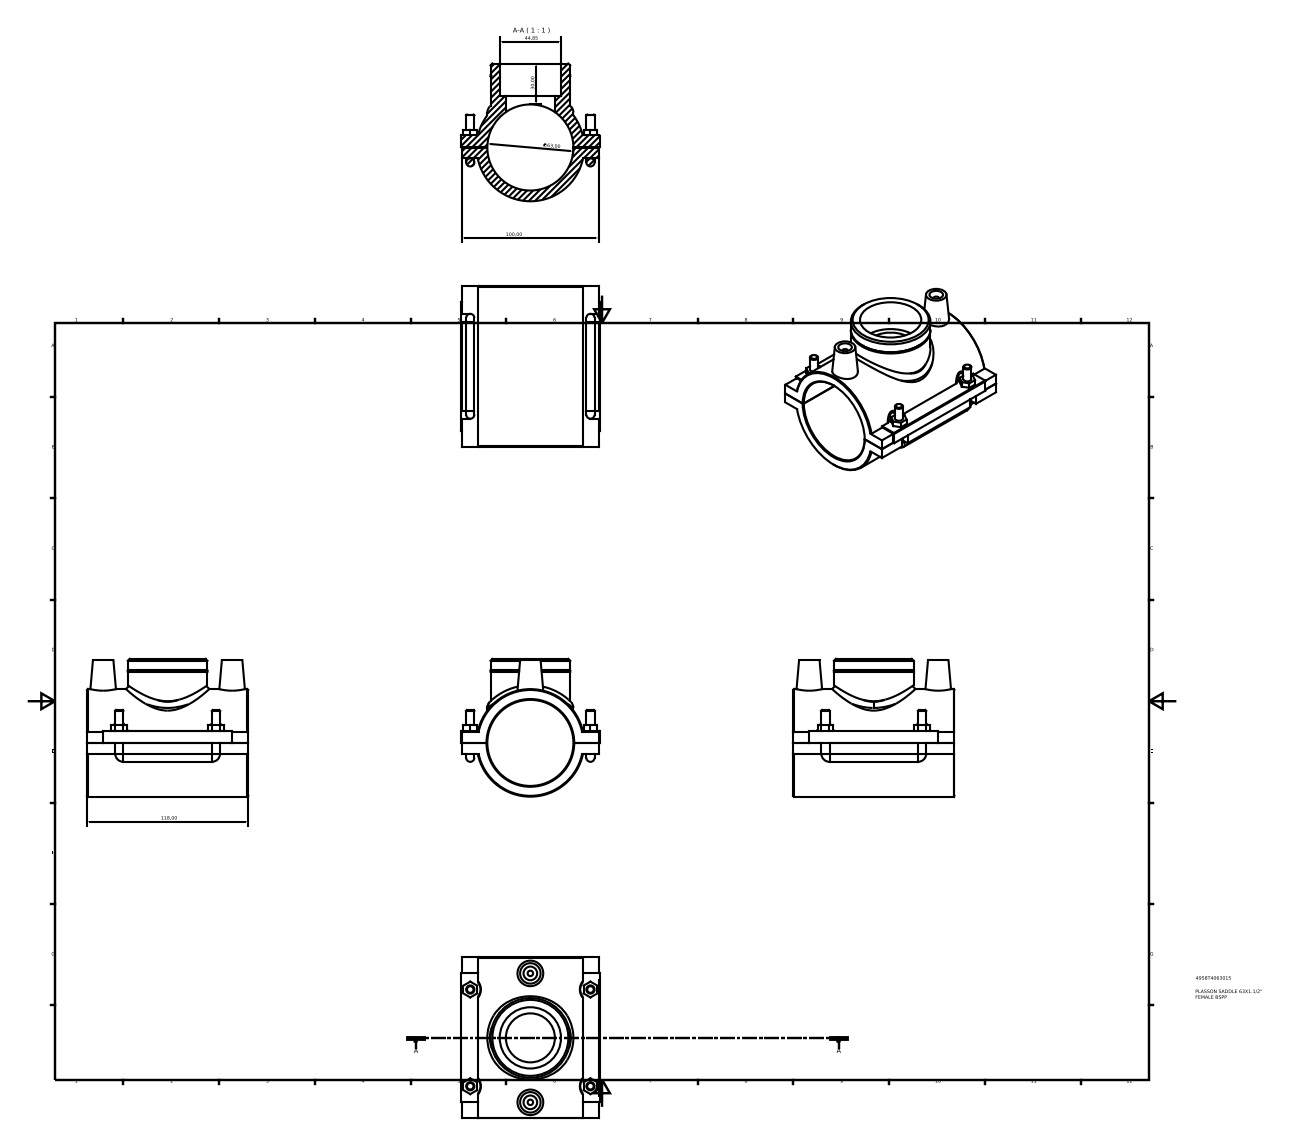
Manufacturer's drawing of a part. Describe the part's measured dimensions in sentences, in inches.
The part is named "4958T4063015". Its 3-D file was written by "Autodesk Inventor 2015 (AUTOMOTIVE_DESIGN)". It is 1 solid with 142 faces: 82 planar, 34 cylindrical and 26 other. Overall it measures 4.646 by 4.016 by 3.972 inches. Its volume is 17.49 cubic inches and its surface area 133.5 square inches. Round holes: 2 of diameter 0.394, 1 of diameter 1.413, 1 of diameter 1.765, 1 of diameter 2.48. Round bosses or shafts: 6 of diameter 0.236, 2 of diameter 0.157, 1 of diameter 3.1, 1 of diameter 2.295, 1 of diameter 2.256. Partial cylindrical surfaces (rounded edges, fillets, slot ends): 4 of radius 0.295, 1 of radius 0.02, 1 of radius 1.24, 1 of radius 1.662. The main face-to-face distances are 0.308, 0.312, 0.039, 0.659, 0.351, 0.347, 4.646, 3.976, 3.937, 2.072. The hole center spacings are 1.858, 3.717.
